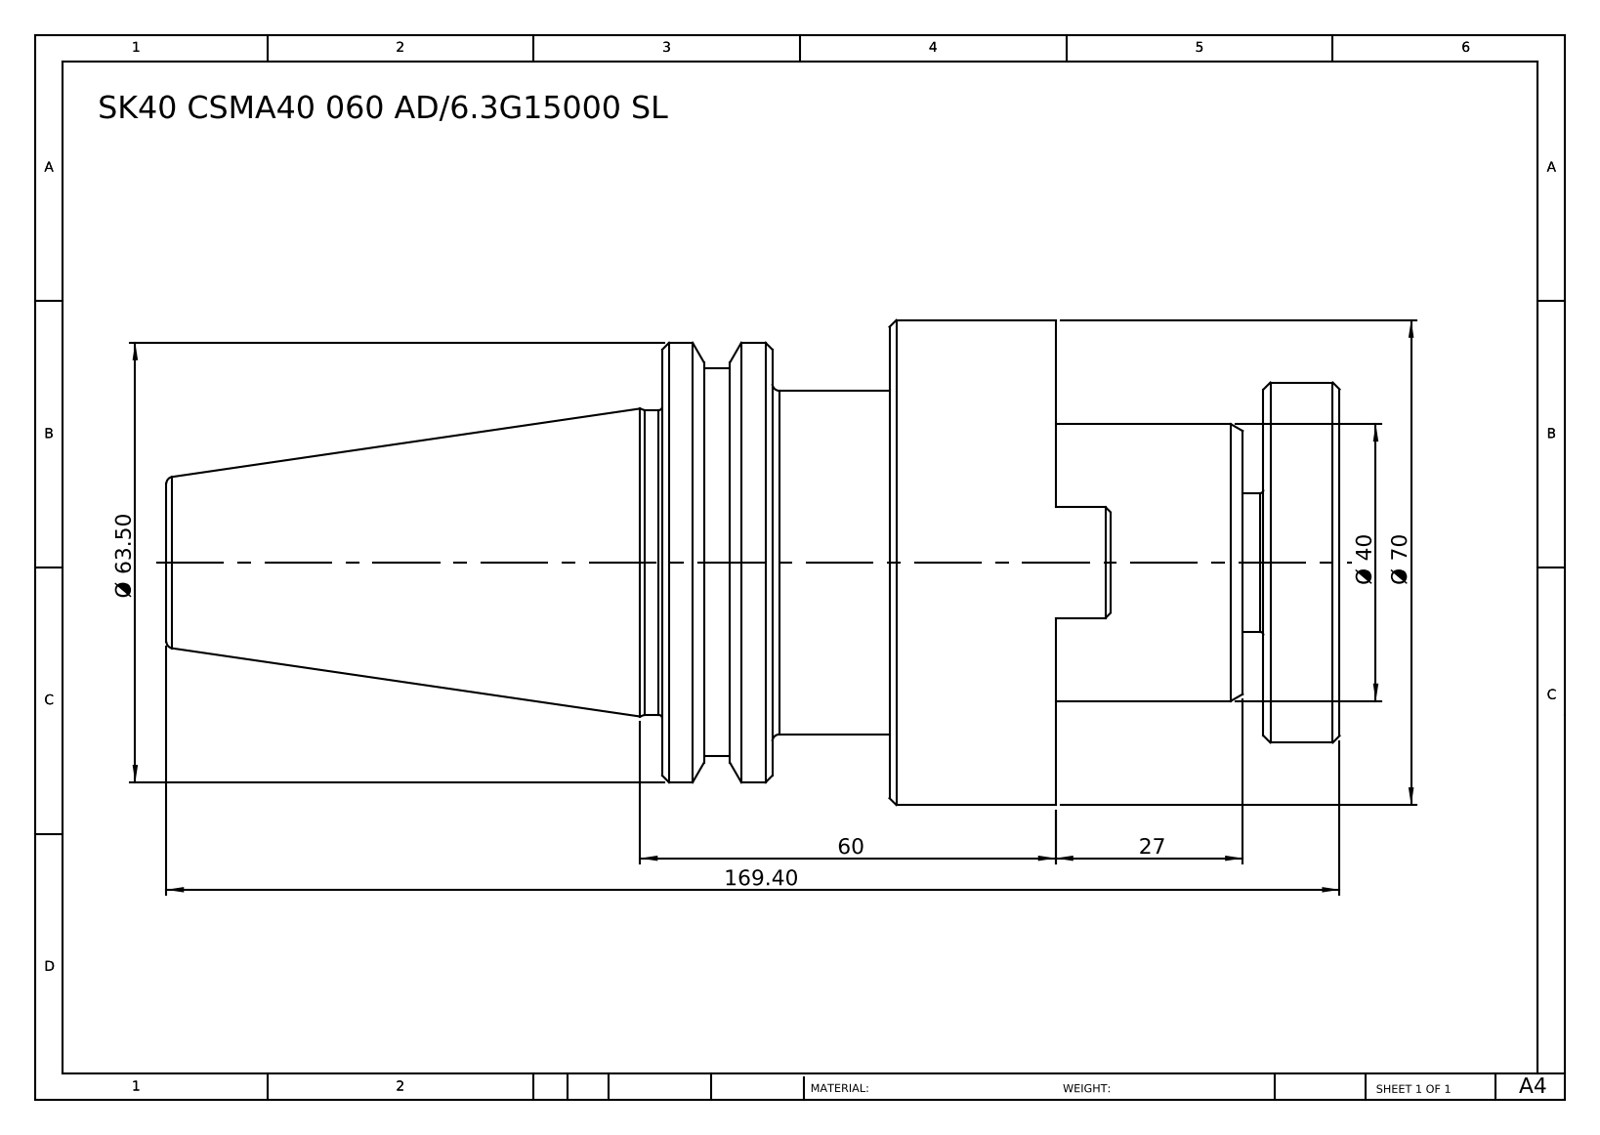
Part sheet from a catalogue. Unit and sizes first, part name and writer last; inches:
Units: inches
Overall size (bounding box): 6.669 × 2.756 × 2.756
Round holes (diameter × count): ⌀1.732 ×1
Round bosses / shafts (diameter × count): ⌀2.756 ×1, ⌀2.5 ×1, ⌀2.205 ×1, ⌀2.047 ×1, ⌀1.954 ×1, ⌀1.575 ×1, ⌀0.787 ×1
Partial cylindrical surfaces — rounded edges, fillets, slot ends (radius × count): R0.197 ×1
Main face-to-face distances: 1.614, 2.559, 0.945, 0.433, 1.181, 2.126, 3.85, 3.417, 2.236, 1.291
Volume: 18.55 in³ · Surface area: 58.96 in²
Bodies: 1 solid, 80 faces (23 planar, 23 cylindrical, 34 other)
Part name (STEP PRODUCT): SK 40 CSMA40 060 AD-6.3G15000 SL SP.S
STEP written by: SolidWorks 2014 (CONFIG_CONTROL_DESIGN)
